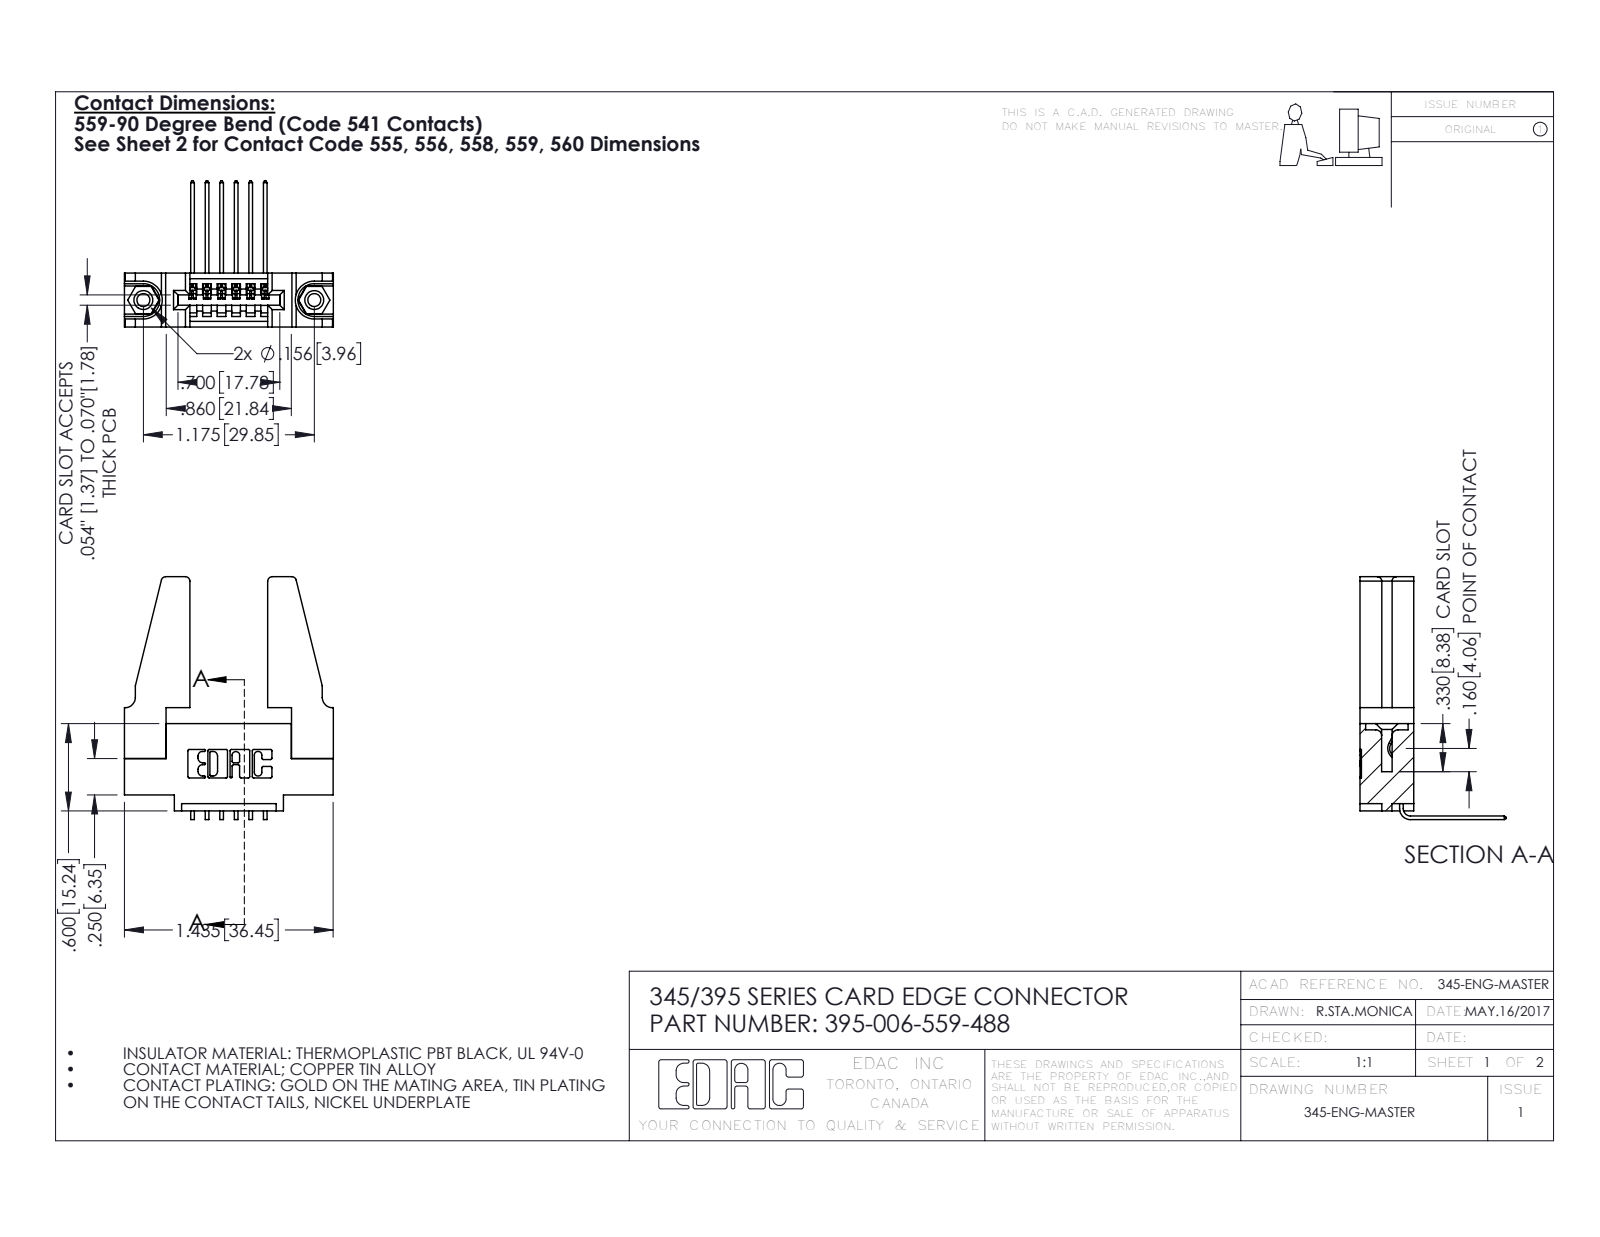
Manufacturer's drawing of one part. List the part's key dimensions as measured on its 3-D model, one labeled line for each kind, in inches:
Part name (STEP PRODUCT): 345-220-078_345-220-088; 395-006-559-488; 345-250-001_345-250-001-102; 345 Part_0.110 Offset - 0.156 Dia-TH (+1 more)
STEP written by: SolidWorks 2016 (CONFIG_CONTROL_DESIGN)
Units: inches
Bodies: 11 solids, 614 faces (408 planar, 190 cylindrical, 16 other)
Overall size (bounding box): 1.669 × 1.436 × 1.005
Volume: 0.389 in³ · Surface area: 10.82 in²
Round holes (diameter × count): ⌀0.089 ×2, ⌀0.125 ×2, ⌀0.156 ×2, ⌀0.064 ×1
Round bosses / shafts (diameter × count): ⌀0.155 ×2
Partial cylindrical surfaces — rounded edges, fillets, slot ends (radius × count): R0.01 ×22, R0.006 ×12, R0.03 ×8, R0.007 ×6, R0.031 ×6, R0.026 ×3, R0.031 ×2, R0.04 ×2
Main face-to-face distances: 0.37, 0.072, 0.298, 0.2, 0.15, 0.148, 0.22, 0.077, 0.45, 0.698
Hole centre spacings: 0.27, 0.946, 1.175
